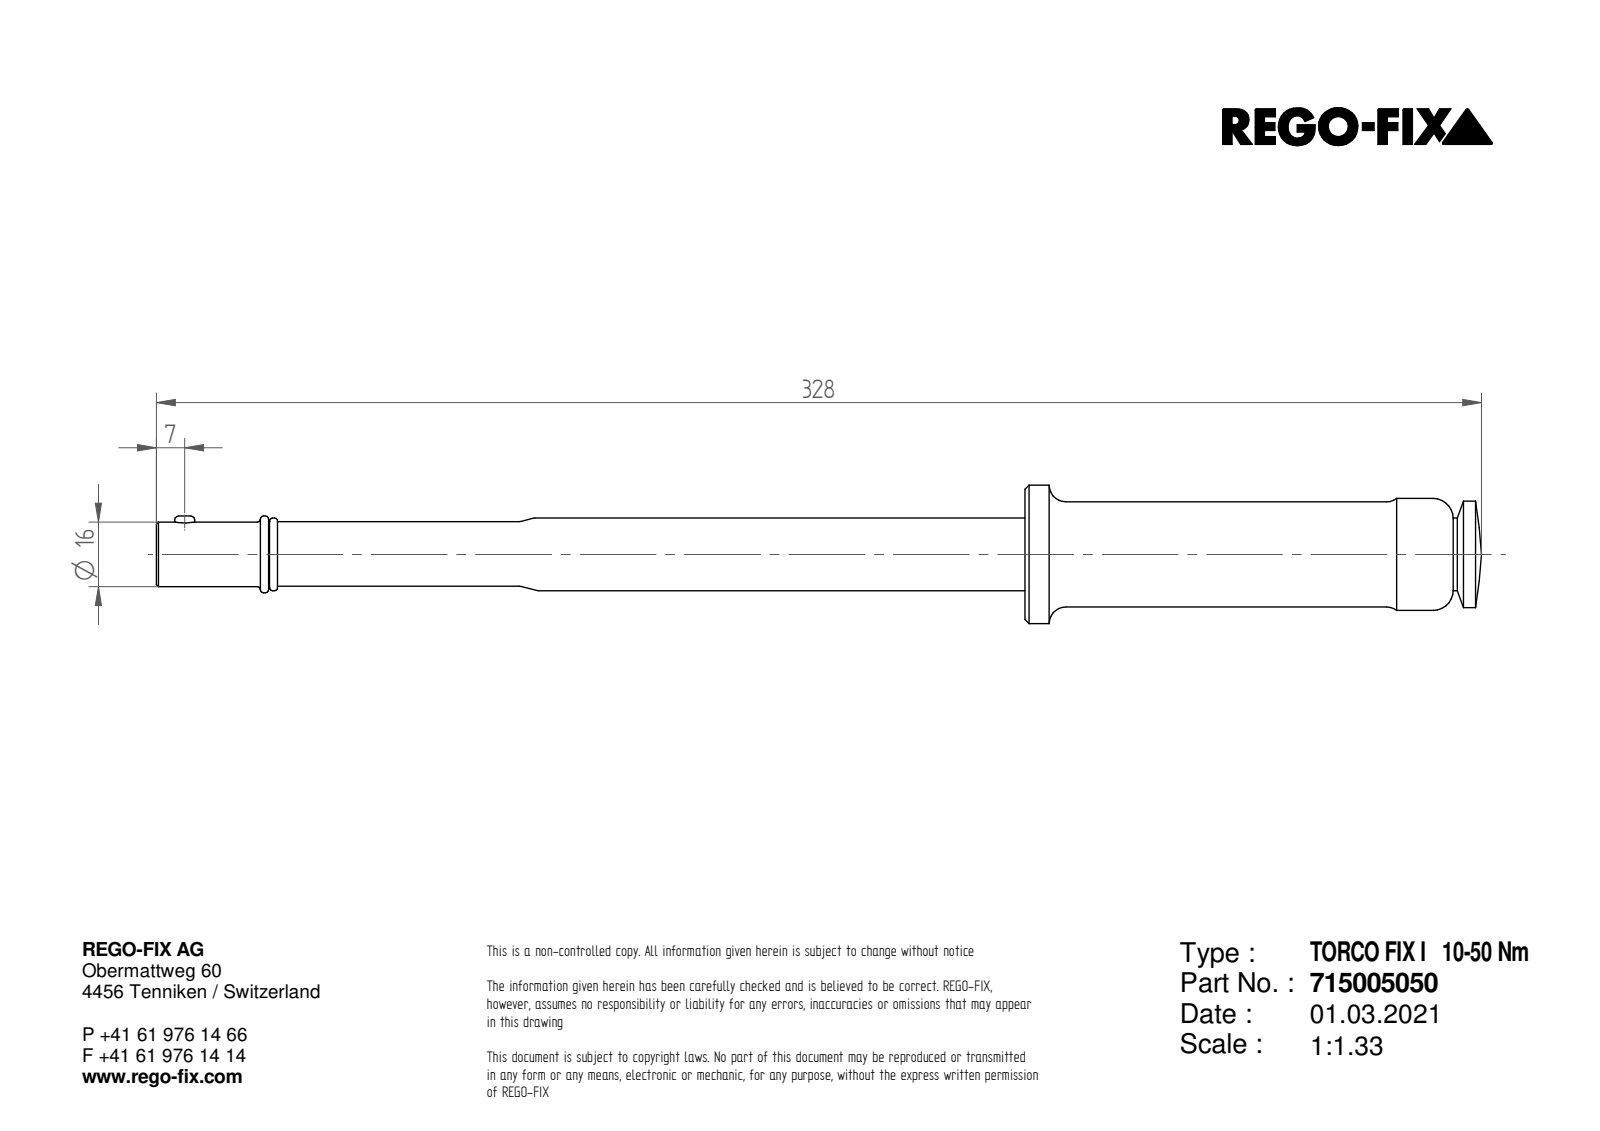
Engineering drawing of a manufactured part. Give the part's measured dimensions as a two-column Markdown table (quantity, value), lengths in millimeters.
| quantity | value |
| --- | --- |
| part name | 6220-1 TORCO-FIX I Adjustable Torque Wrench 10-50 Nm (16mm interface); 6220-2 TORCO-FIX I Adjustable Torque Wrench 10-50 Nm (16mm interface); 6220 TORCO-FIX I Adjustable Torque Wrench 10-50 Nm (16mm interface) |
| STEP written by | Alibre (AUTOMOTIVE_DESIGN) |
| units | millimeters |
| bodies | 2 solids, 60 faces (18 planar, 20 cylindrical, 22 other) |
| overall size | 328 × 34.25 × 34.25 |
| volume | 137 328 mm³ |
| surface area | 29 528 mm² |
| round bosses / shafts (diameter × count) | 34.25 × 1, 27.7 × 1, 26.75 × 1, 26.4 × 1, 26 × 1, 19 × 1, 18 × 1, 16.25 × 1 |
| partial cylindrical surfaces (radius × count) | 2 × 6, 20 × 1 |
| main face-to-face distances | 14.25, 16, 1.75, 215, 140, 75, 30, 110, 185, 27.75 |
